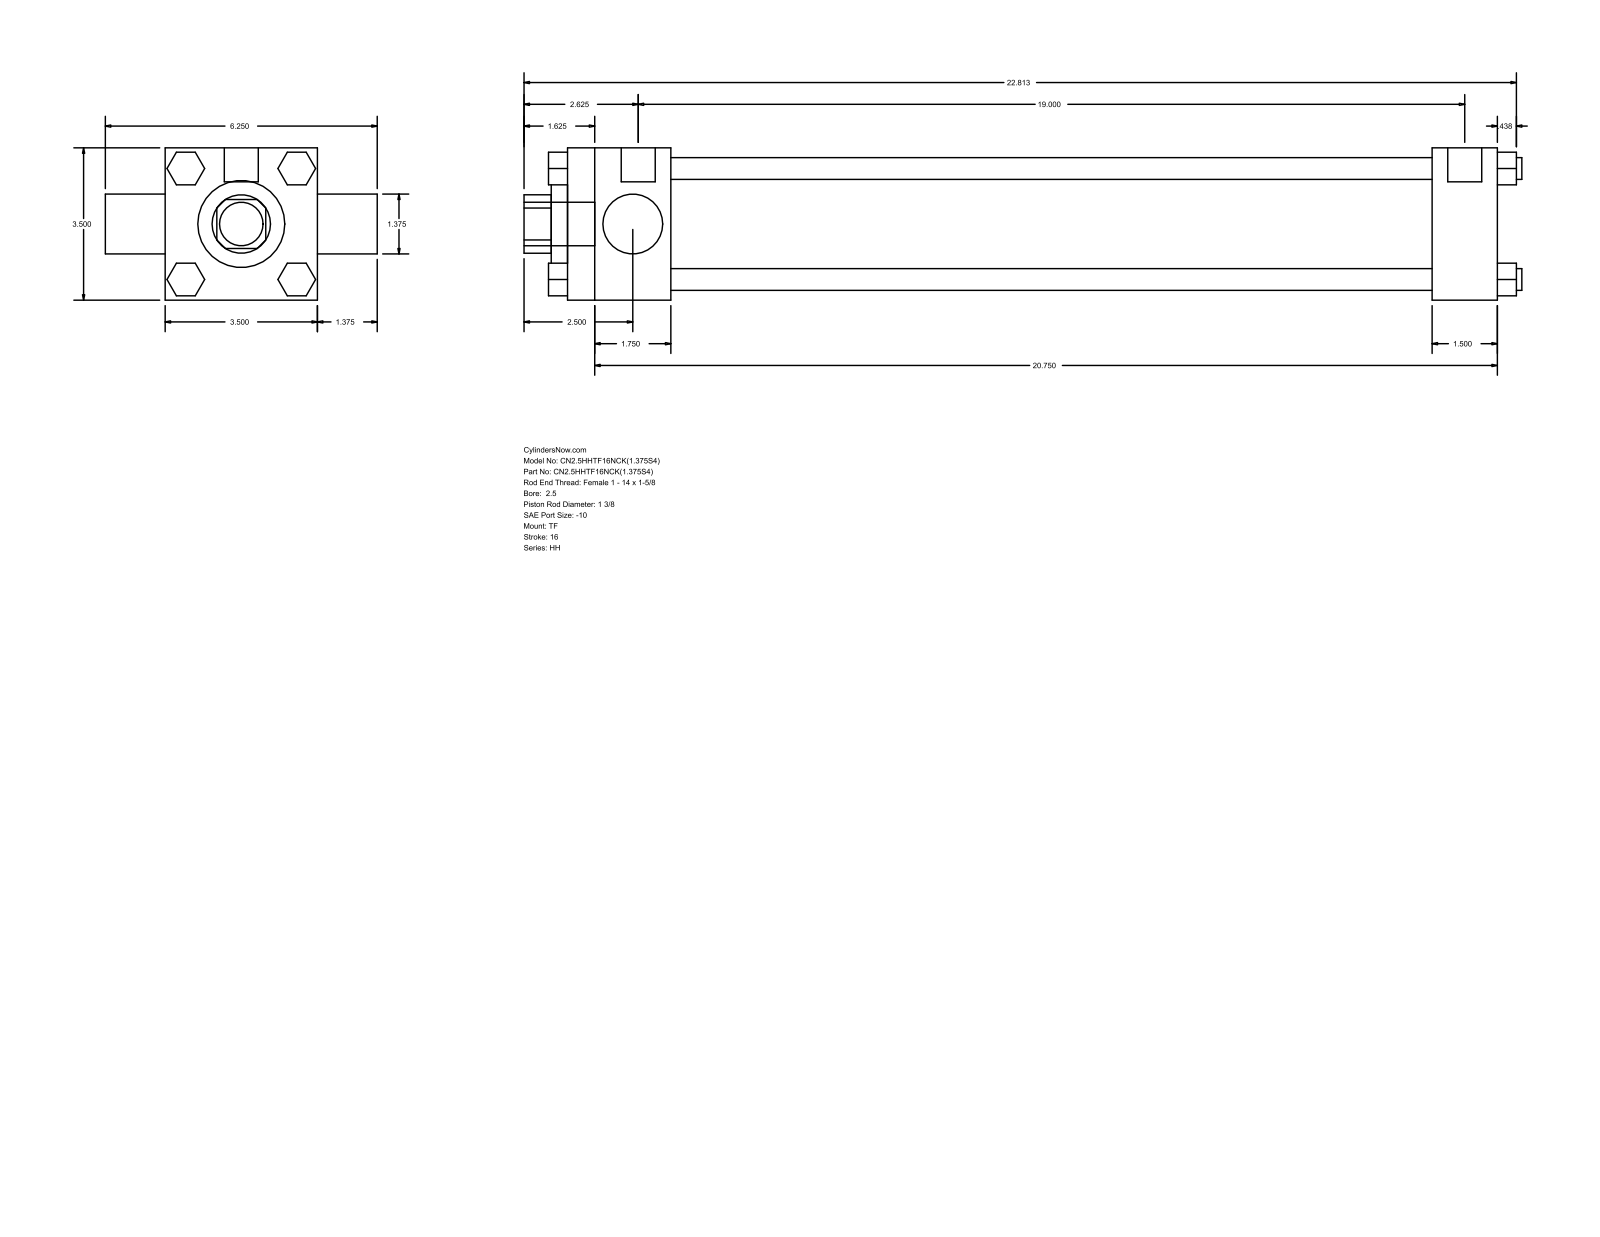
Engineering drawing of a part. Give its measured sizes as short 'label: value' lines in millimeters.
name: HH_TF__0250_1.375
written by: GSSL Pune (CONFIG_CONTROL_DESIGN)
unit: mm
bodies: 0 solids, 120 faces (92 planar, 28 cylindrical, 0 other)
size: 582.61 × 158.75 × 88.9
holes: 2× ⌀34.92, 1× ⌀50.8, 1× ⌀73.03
bosses: 4× ⌀12.7, 3× ⌀5.56, 2× ⌀19.84, 1× ⌀25.4
rounds: 1× R17.06
face distances: 88.9, 542.93, 60.32, 482.61, 504.83, 444.51, 38.1, 19.05, 32.38, 56.09
